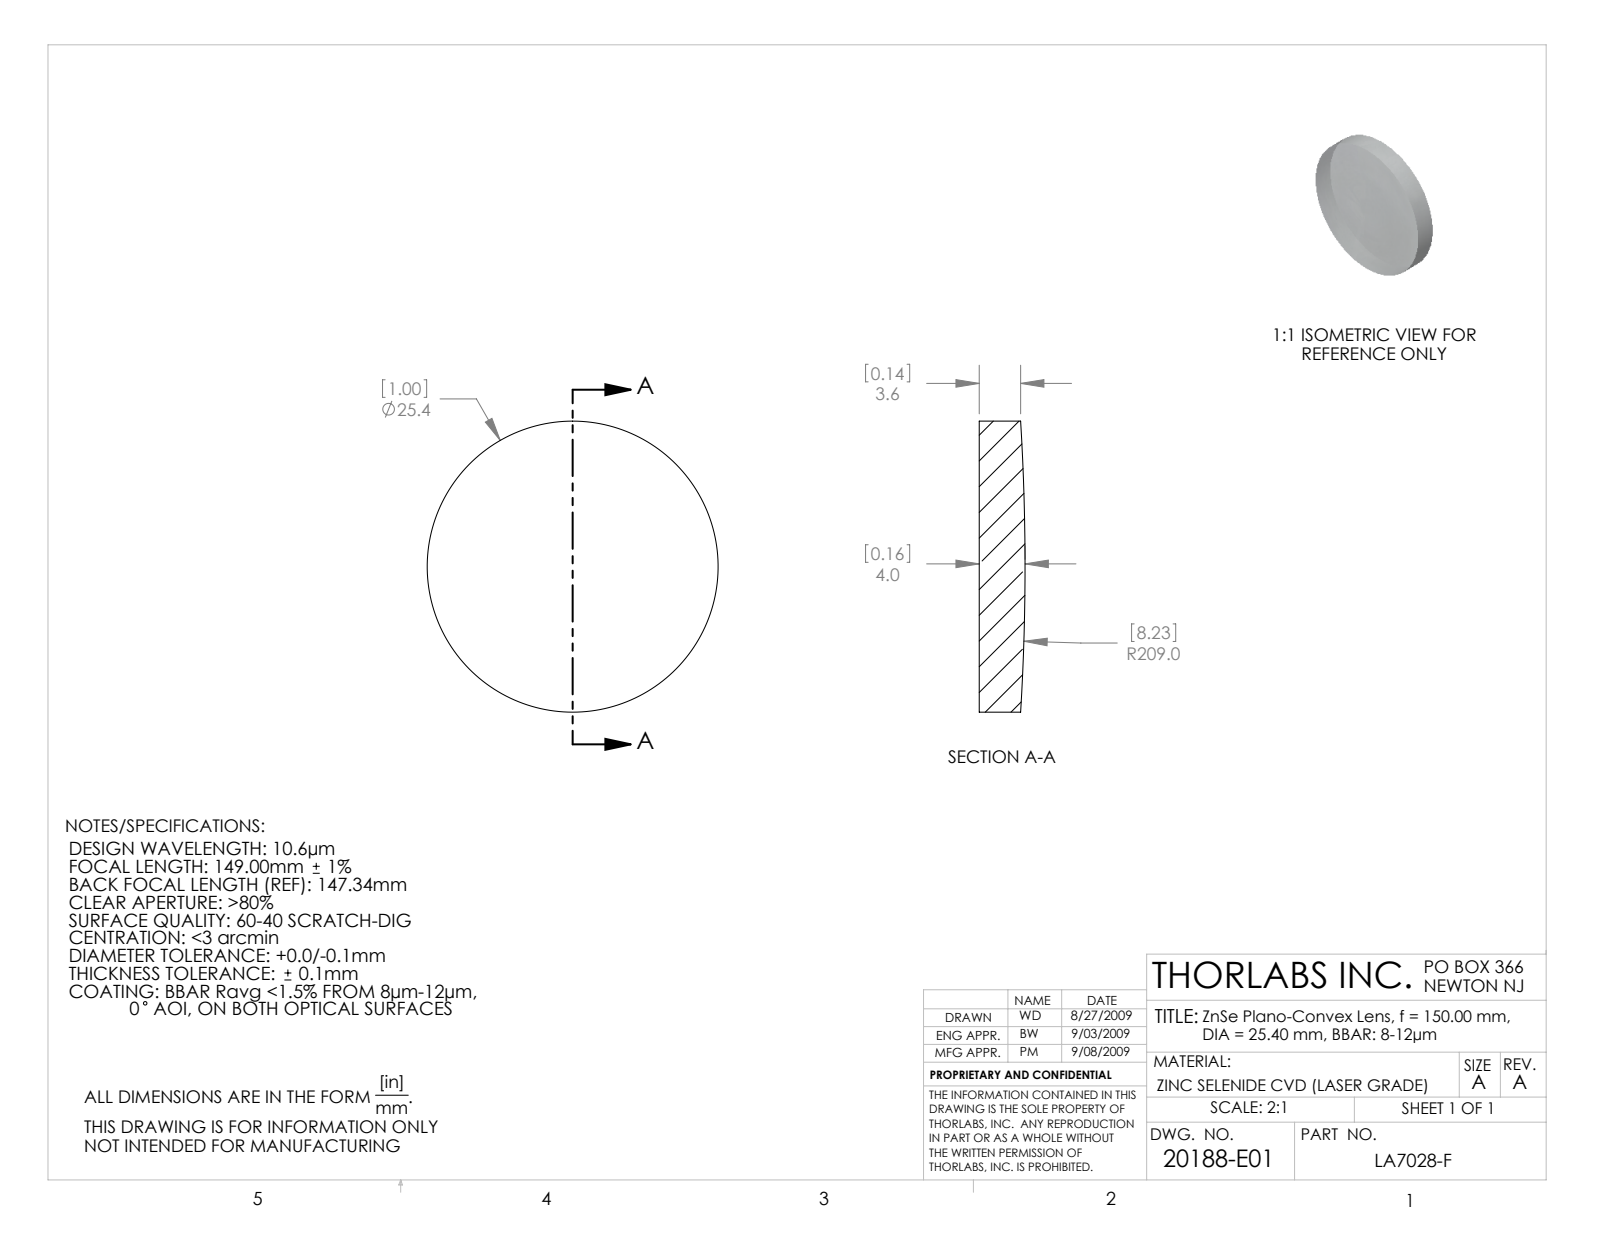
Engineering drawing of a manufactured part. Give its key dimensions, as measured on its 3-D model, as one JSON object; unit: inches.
{"part_name": "20188-E0W", "step_written_by": "SolidWorks 2007 (CONFIG_CONTROL_DESIGN)", "units": "inches", "bodies": {"solids": 1, "faces": 5, "planar": 1, "cylindrical": 2, "other": 2}, "overall_size": [1, 1, 0.157], "volume_in3": 0.118, "surface_area_in2": 2.018, "round_bosses_or_shafts": [[1, 1]]}
